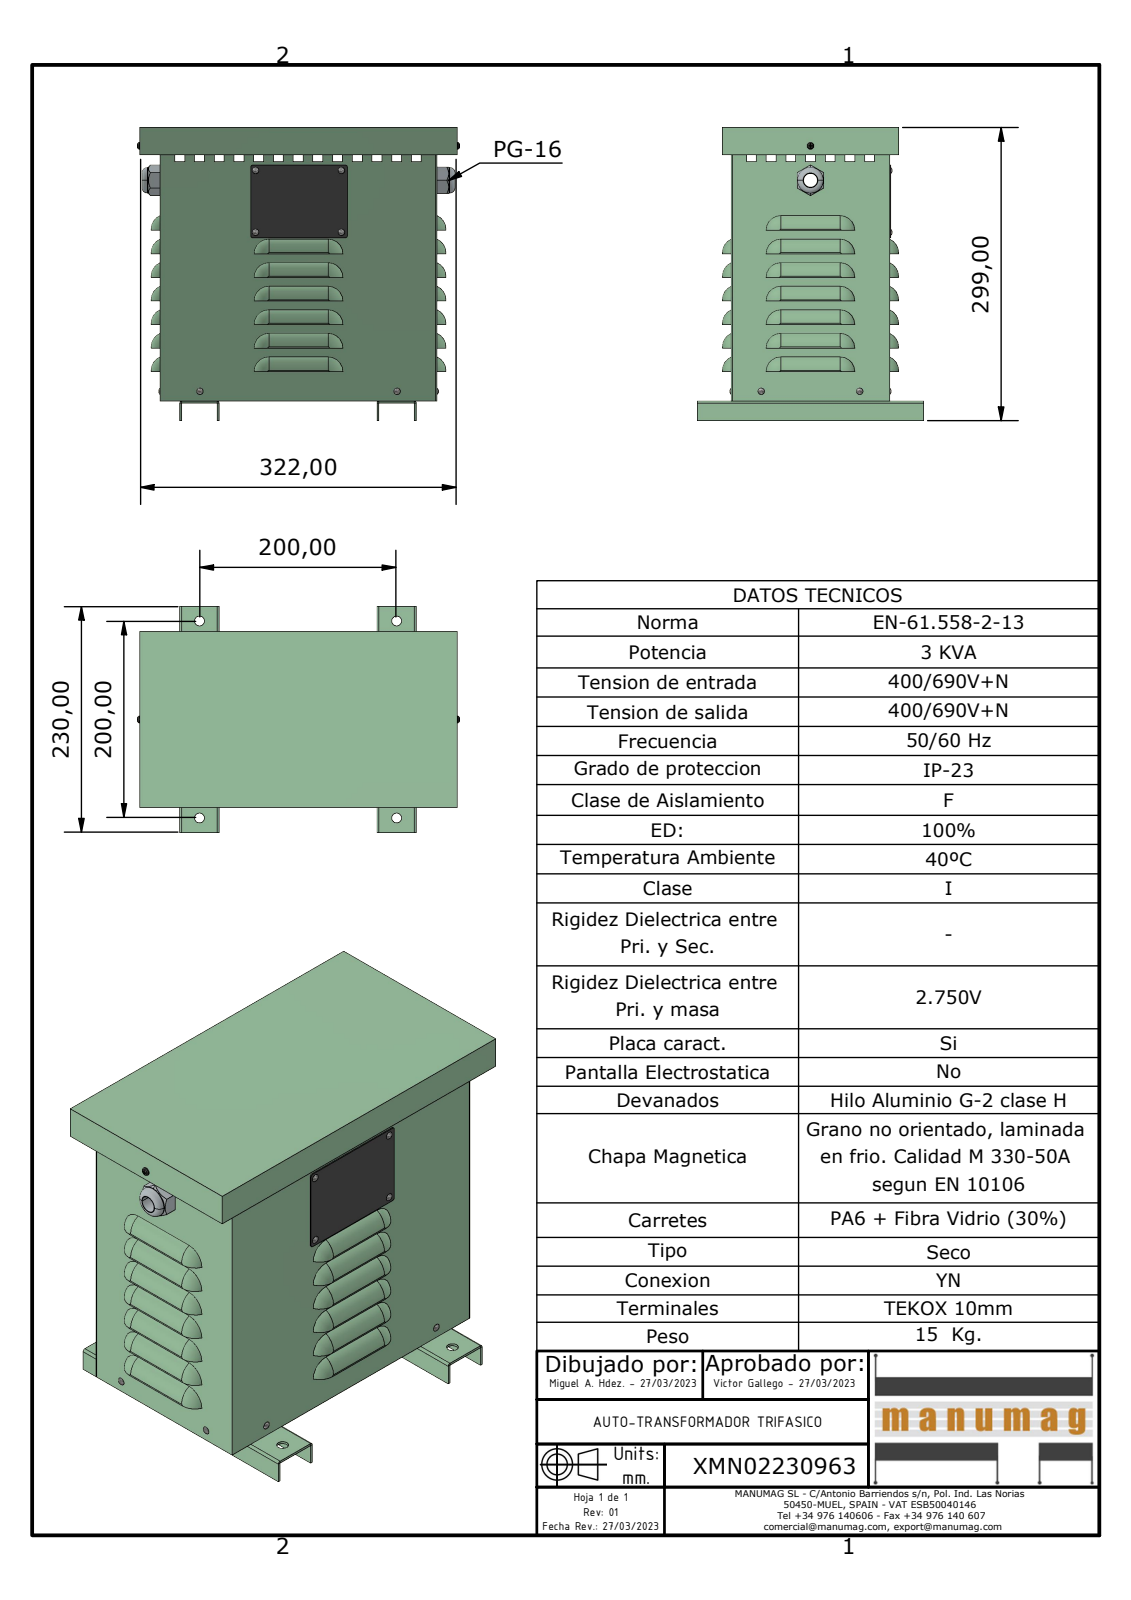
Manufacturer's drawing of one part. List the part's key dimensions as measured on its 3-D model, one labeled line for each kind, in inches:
Part name (STEP PRODUCT): XMN02230963; JE003 - JE004 - JE005 NACIONAL CUERPO; JE003 - JE004 - JE005 NACIONAL BASE; PLACA CARACTERISTICAS (+5 more)
STEP written by: Autodesk Inventor 2023 (AUTOMOTIVE_DESIGN)
Units: inches
Bodies: 22 solids, 1061 faces (647 planar, 228 cylindrical, 186 other)
Overall size (bounding box): 12.88 × 11.776 × 9.055
Volume: 48.19 in³ · Surface area: 1 385 in²
Round holes (diameter × count): ⌀0.157 ×9, ⌀0.394 ×4, ⌀0.118 ×1, ⌀0.551 ×1, ⌀0.945 ×1
Round bosses / shafts (diameter × count): ⌀0.126 ×8, ⌀1.024 ×1, ⌀0.906 ×1, ⌀0.886 ×1, ⌀0.138 ×1, ⌀0.125 ×1
Partial cylindrical surfaces — rounded edges, fillets, slot ends (radius × count): R0.276 ×26, R0.551 ×26, R0.591 ×26, R0.059 ×18, R0.197 ×8, R0.217 ×8, R0.118 ×6, R0.079 ×4
Main face-to-face distances: 0.059, 6.28, 10.93, 6.22, 6.339, 11.004, 10.989, 10.945, 0.354, 6.634
Hole centre spacings: 7.874, 2.48, 3.425, 4.229, 6.755, 8.52, 8.691, 9.133
